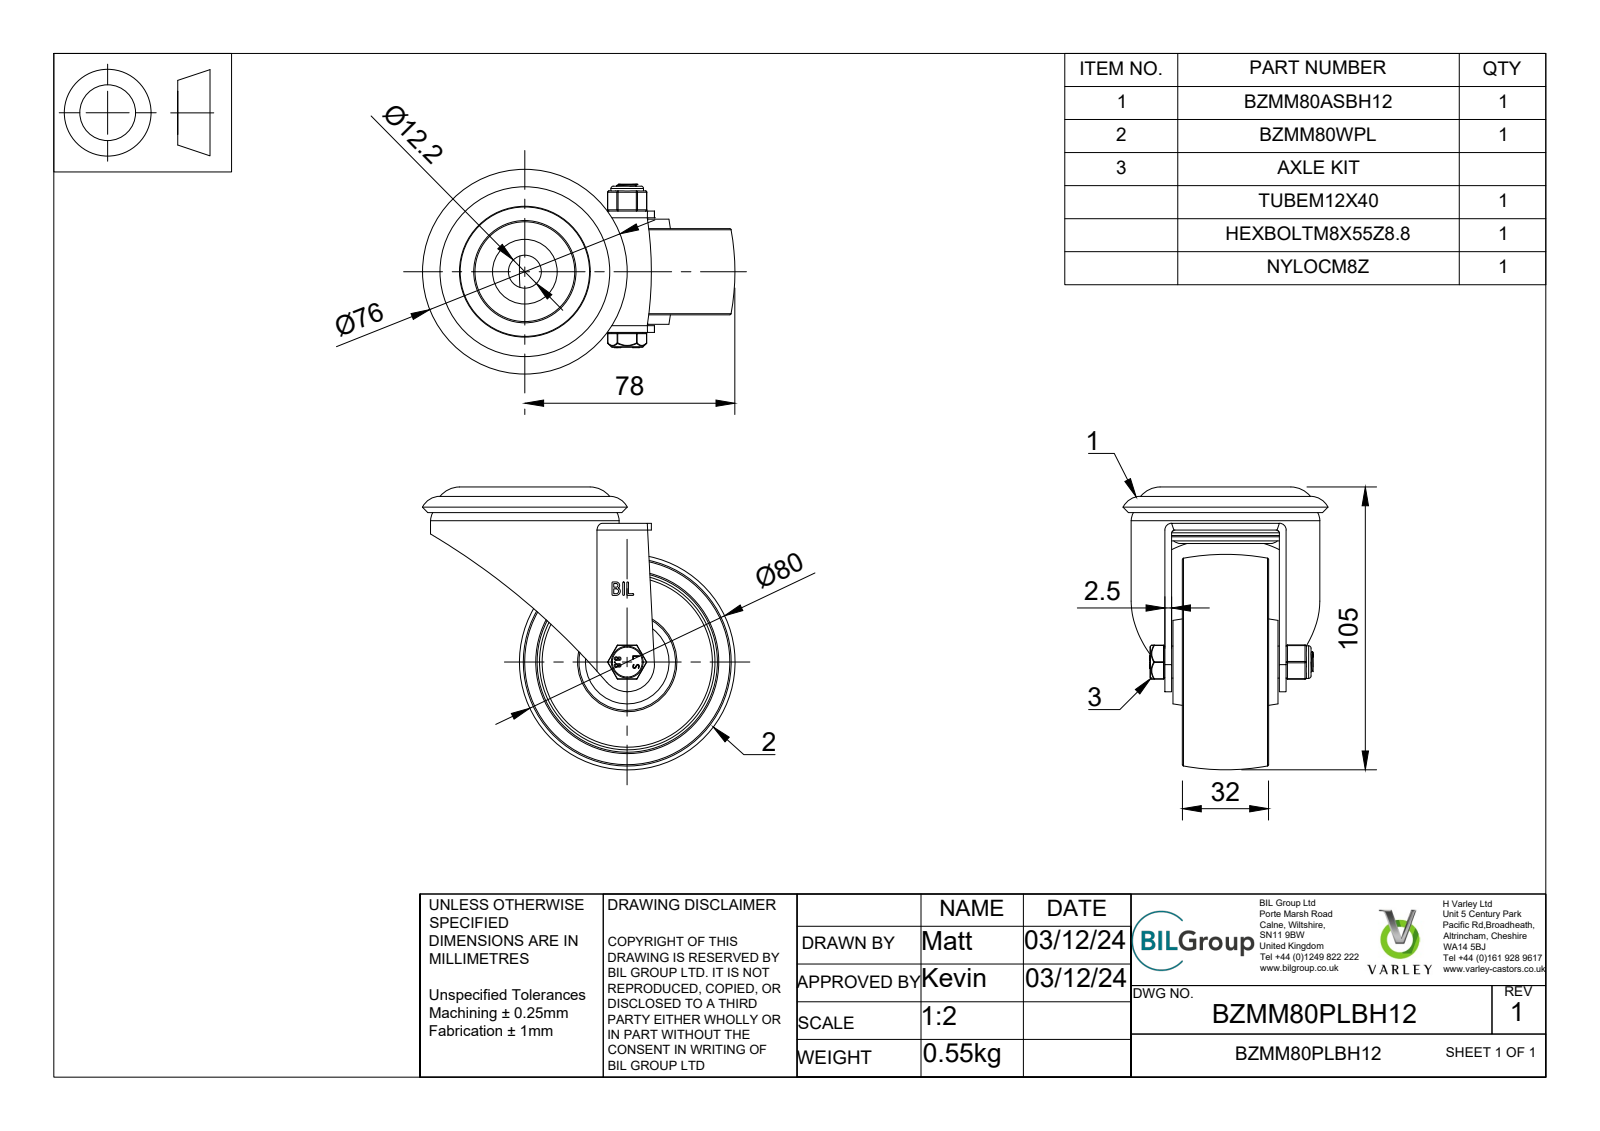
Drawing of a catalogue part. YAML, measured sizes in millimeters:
part_name: "BZMM80PLBH12 v3; BZMM80ASBH12 v1; ZINC PLATED, PRESSED STEEL FORKS; ZINC PLATED, PRESSED STEEL TOP PLATE (+8 more)"
step_written_by: "Autodesk Translation Framework v13.20.0.188 (AP242_MANAGED_MODEL_BASED_3D_ENGINEERING_MIM_LF)"
units: millimeters
bodies: {solids: 7, faces: 341, planar: 109, cylindrical: 124, other: 108}
overall_size: [116, 105, 76]
volume: 151897
surface_area: 72003
round_holes:
  - {diameter: 0.66, count: 2}
  - {diameter: 12.2, count: 2}
  - {diameter: 8, count: 1}
  - {diameter: 8.2, count: 1}
  - {diameter: 8.4, count: 1}
  - {diameter: 8.6, count: 1}
  - {diameter: 65, count: 1}
  - {diameter: 72, count: 1}
round_bosses_or_shafts:
  - {diameter: 70, count: 1}
  - {diameter: 49.5, count: 1}
  - {diameter: 38, count: 1}
  - {diameter: 24, count: 1}
  - {diameter: 21.31, count: 1}
  - {diameter: 12.1, count: 1}
  - {diameter: 11.9, count: 1}
  - {diameter: 11.5, count: 1}
partial_cylinders:
  - {radius: 0.5, count: 18}
  - {radius: 0.25, count: 12}
  - {radius: 0.33, count: 4}
  - {radius: 0.64, count: 4}
  - {radius: 1.25, count: 4}
  - {radius: 0.63, count: 2}
  - {radius: 0.64, count: 2}
  - {radius: 2.5, count: 2}
face_to_face_distances: [2.5, 7, 4, 6.5, 19, 26, 16.5, 42.5, 23.5, 36]
hole_center_spacings: [3.22, 2.49]
